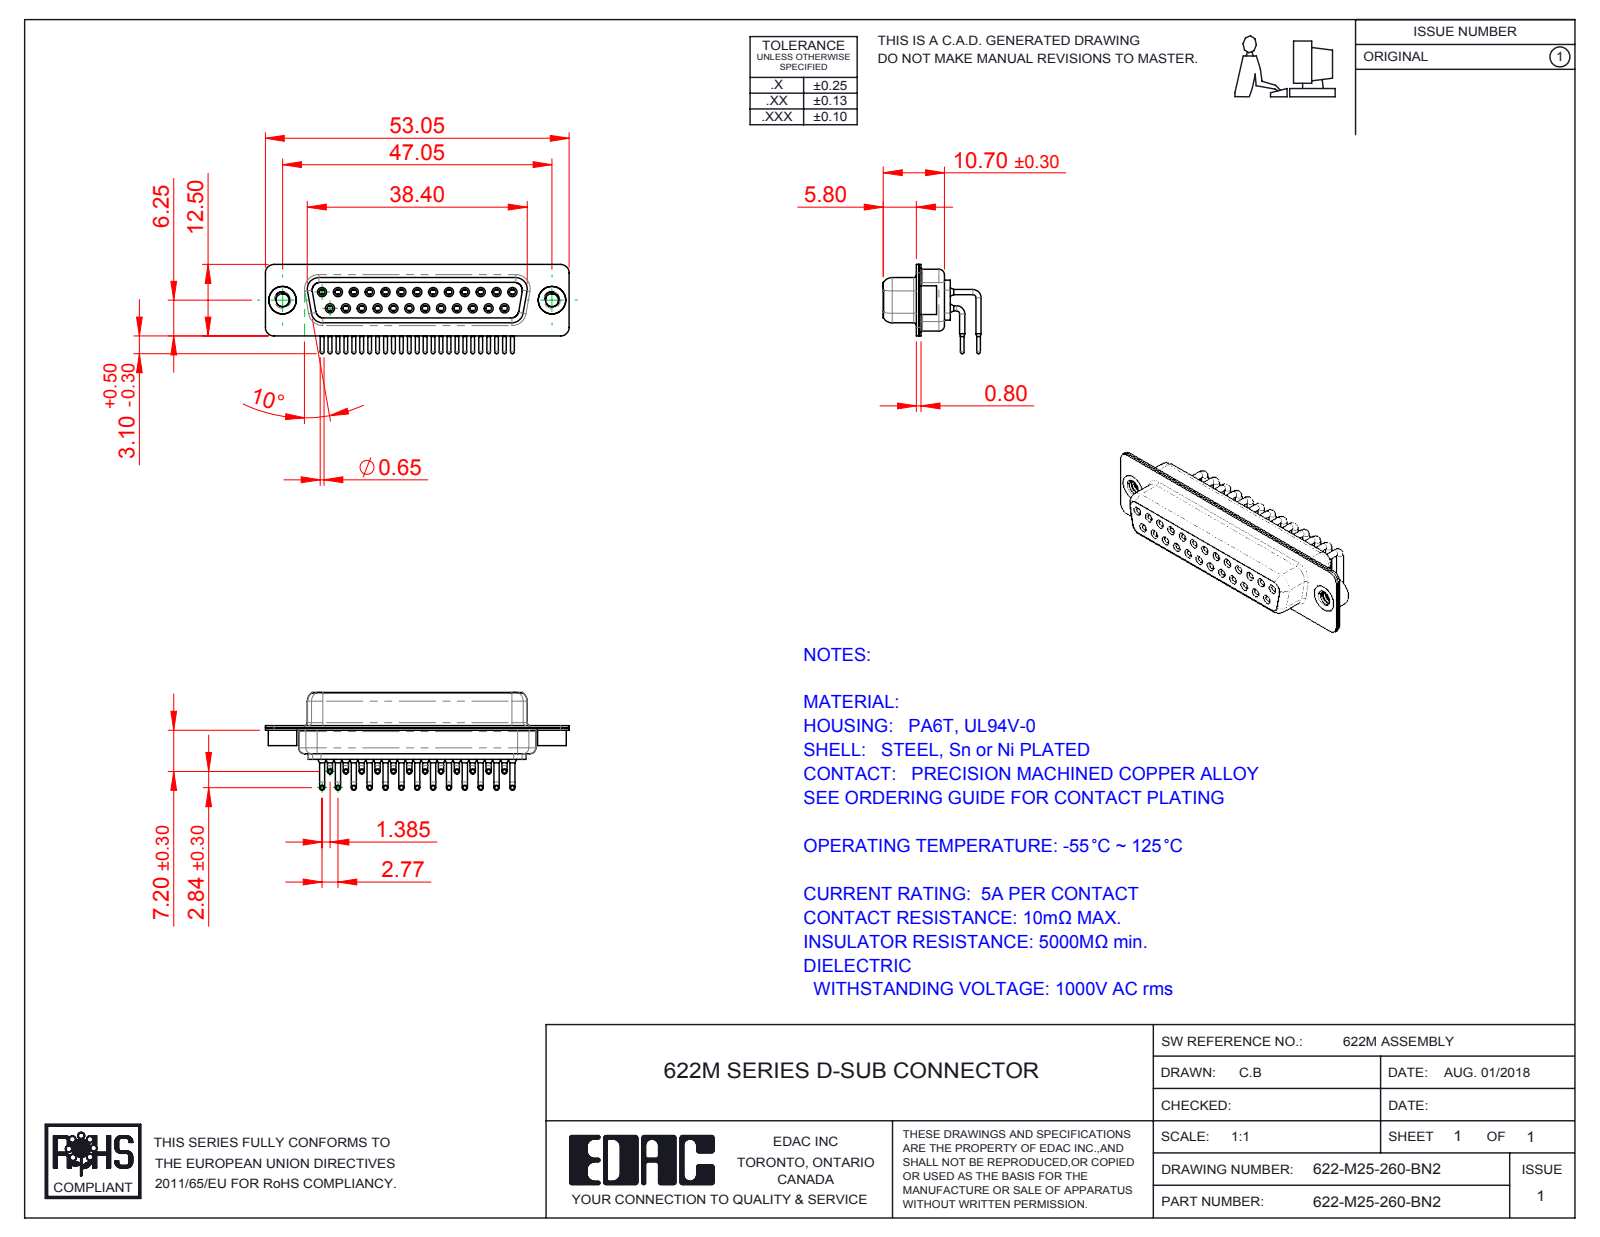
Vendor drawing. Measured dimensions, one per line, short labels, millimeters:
name: 622-M25-260-BN2; 622M 4-40 Threaded Rivet; 622M Contact Row 2; 622M Contact Row 1 (+3 more)
written by: SolidWorks 2016 (CONFIG_CONTROL_DESIGN)
unit: mm
bodies: 30 solids, 1604 faces (442 planar, 712 cylindrical, 450 other)
size: 53.05 × 17.09 × 15.6
volume: 3 852 mm³; area: 9 502 mm²
holes: 25× ⌀1, 25× ⌀1.1, 25× ⌀1.7, 25× ⌀1.8, 25× ⌀2, 2× ⌀2.26, 2× ⌀4, 2× ⌀4.8
bosses: 50× ⌀0.9, 25× ⌀1.6, 25× ⌀1.5, 25× ⌀0.65, 2× ⌀5, 2× ⌀4.9
rounds: 16× R1.5, 12× R2, 8× R1.35, 8× R1.6, 4× R0.25, 4× R0.5, 4× R0.6, 4× R0.65
face distances: 0.4, 1.45, 8.95, 6.2, 2.3, 1.9, 8.5, 0.45, 7.05, 0.85
hole spacings: 3.16, 2.77, 5.54, 8.31, 11.08, 13.85, 16.62, 5.03
